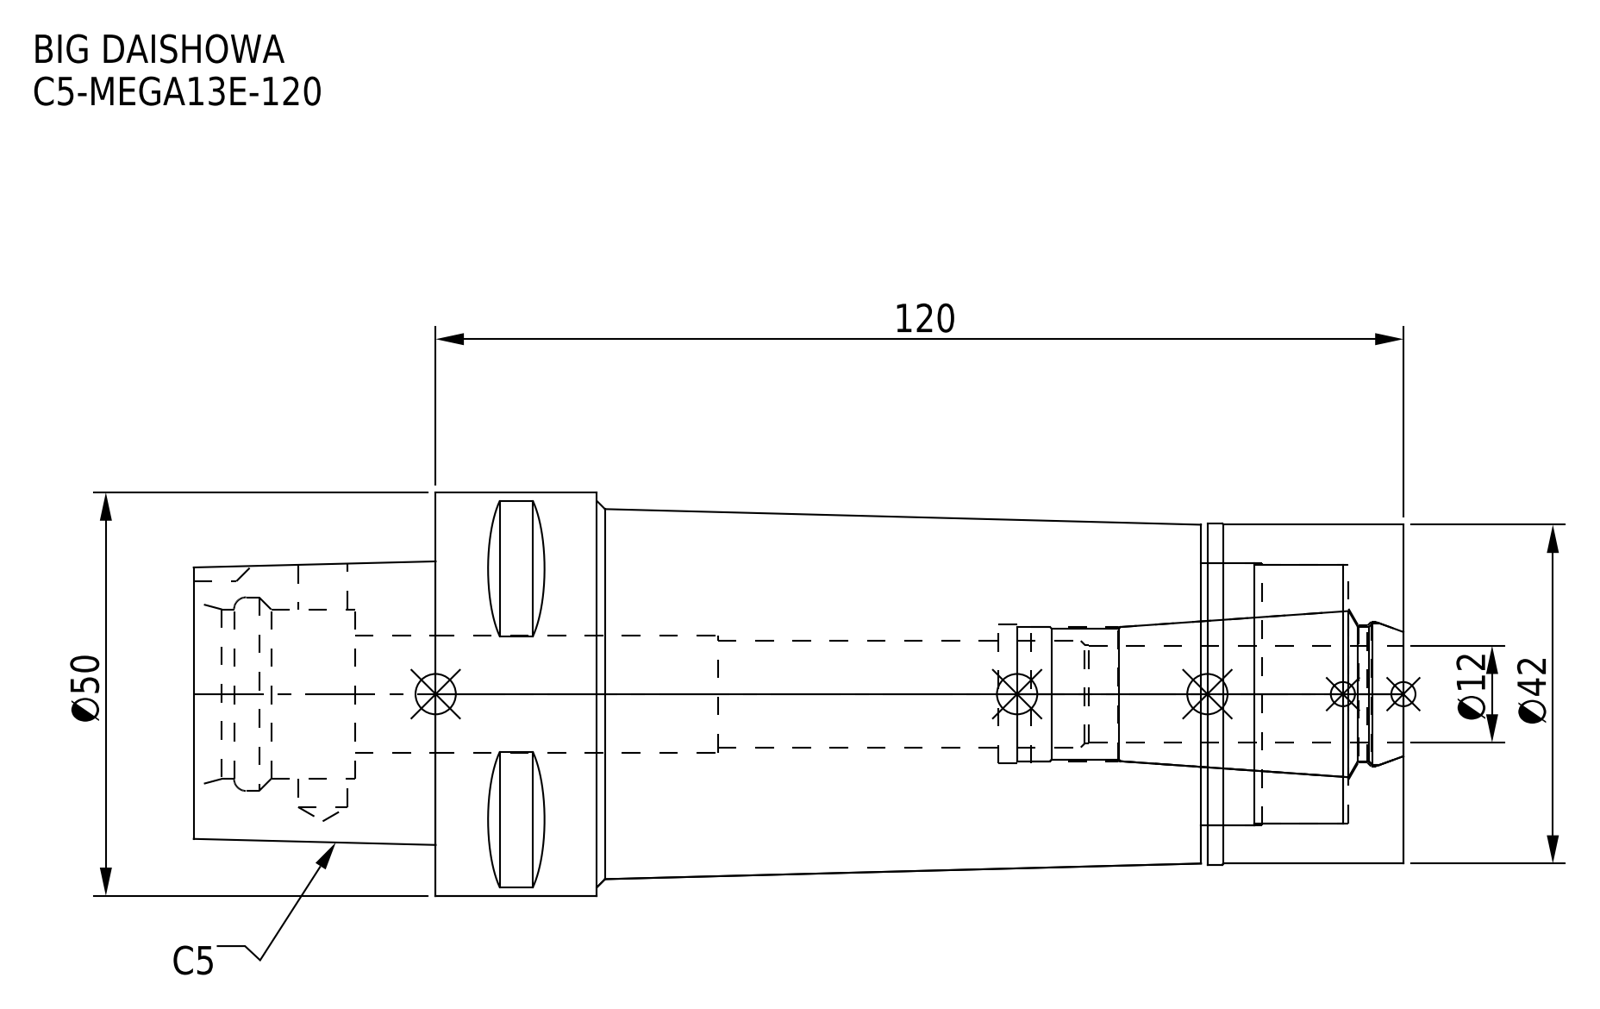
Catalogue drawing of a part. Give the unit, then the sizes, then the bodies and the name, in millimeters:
Units: millimetres
Overall size (bounding box): 150 × 50 × 50
Round holes (diameter × count): ⌀6.1 ×1, ⌀13.3 ×1, ⌀14.5 ×1, ⌀16.6 ×1, ⌀17 ×1, ⌀17.2 ×1, ⌀17.9 ×1, ⌀21 ×1, ⌀24 ×1, ⌀32 ×1, ⌀32.5 ×1
Round bosses / shafts (diameter × count): ⌀50 ×1, ⌀42.3 ×1, ⌀42 ×1
Partial cylindrical surfaces — rounded edges, fillets, slot ends (radius × count): R4 ×1
Main face-to-face distances: 120, 25.1, 24.3, 95.7, 0.8, 94.9, 30, 112.5, 6.8, 17.5
Volume: 181 036 mm³ · Surface area: 37 003 mm²
Bodies: 2 solids, 97 faces (36 planar, 37 cylindrical, 24 other)
Part name (STEP PRODUCT): C5-MEGA13E-120_1.stp; C5-MEGA13E-120-120-FreeParts; DXF_TEMP_ASSY_ASM_4_ASM.stp; C5-MEGA13E-120-120_ASM.stp (+3 more)
STEP written by: SolidWorks 2019 (CONFIG_CONTROL_DESIGN)
